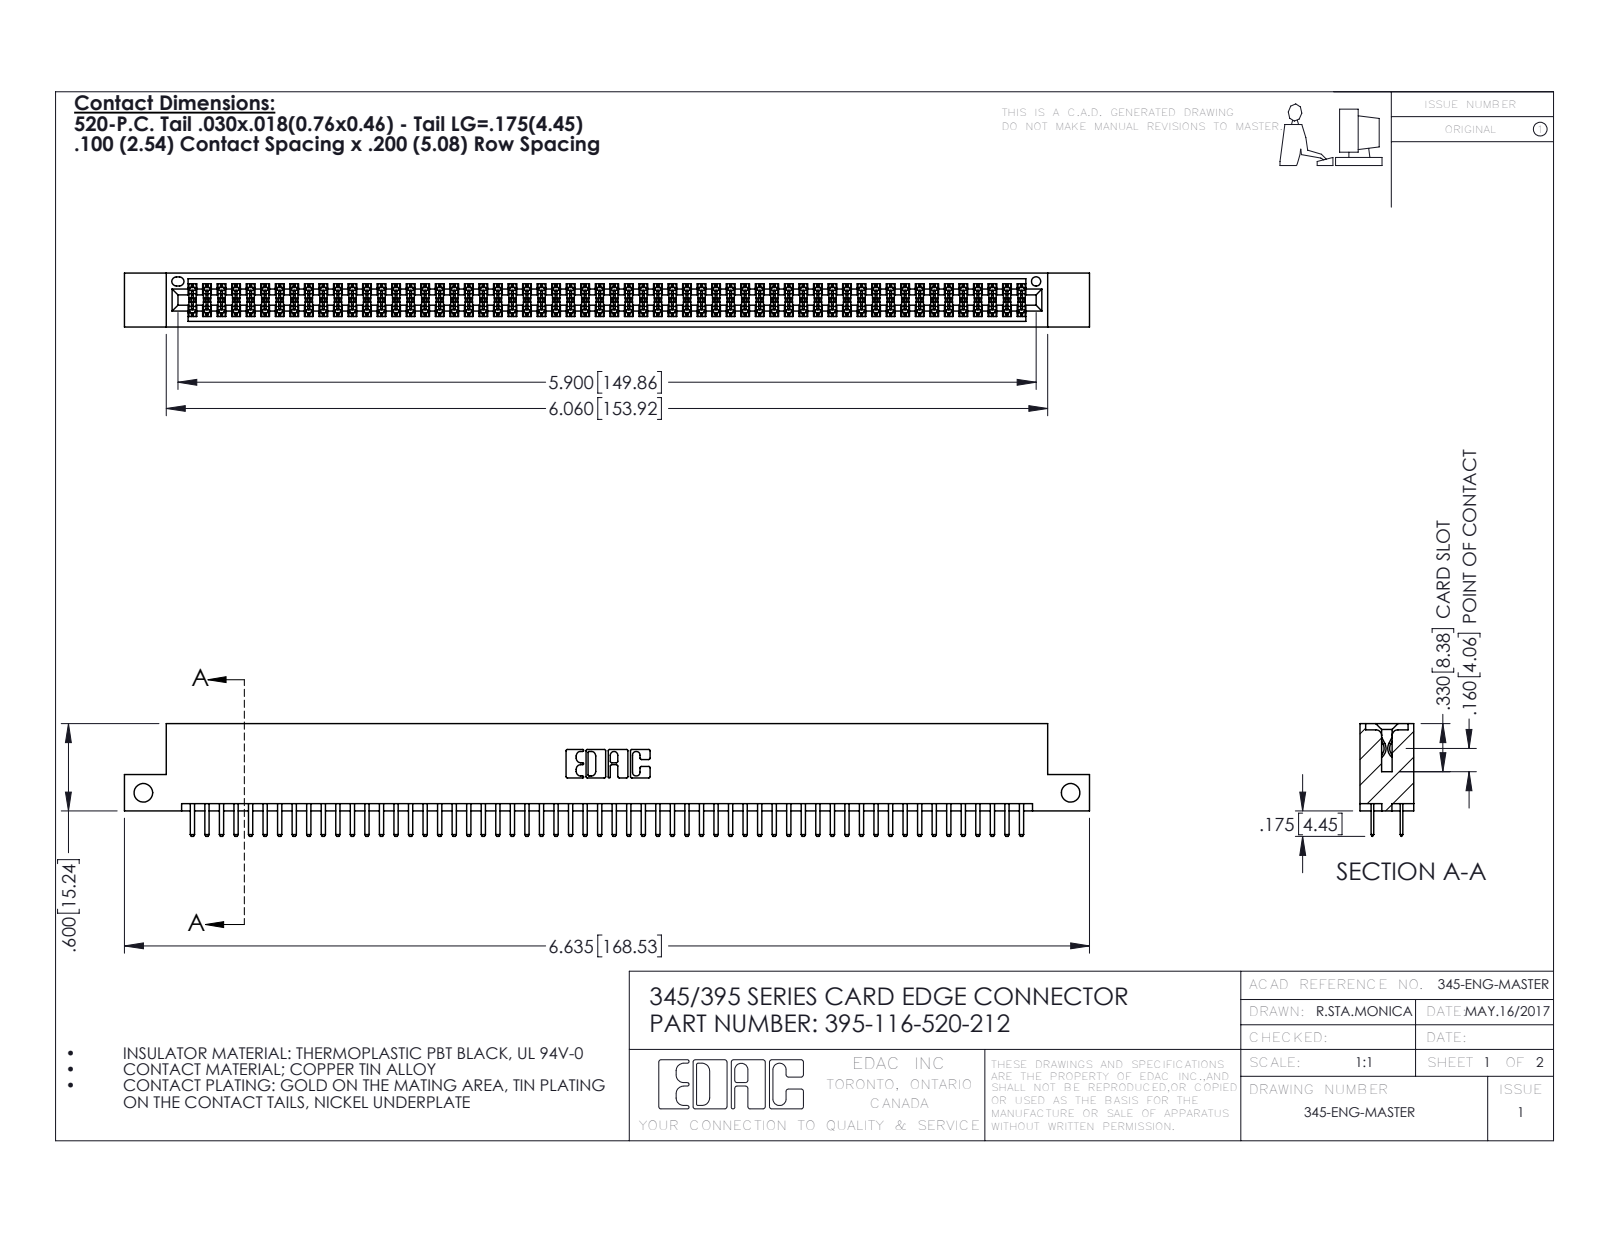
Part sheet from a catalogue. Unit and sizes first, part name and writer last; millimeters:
Units: millimetres
Overall size (bounding box): 168.5 × 19.7 × 9.4
Round holes (diameter × count): ⌀3.3 ×2, ⌀1.6 ×1
Partial cylindrical surfaces — rounded edges, fillets, slot ends (radius × count): R0.2 ×174, R0.3 ×120, R0.3 ×22, R0.2 ×6, R0.8 ×6, R0.7 ×3, R0.4 ×2, R0.5 ×2
Main face-to-face distances: 7.6, 1.8, 5.1, 9.4, 2.5, 6.9, 0.6, 5.7, 0.6, 1.8
Hole centre spacings: 161.9
Volume: 16 390 mm³ · Surface area: 24 280 mm²
Bodies: 117 solids, 6390 faces (4140 planar, 2250 cylindrical, 0 other)
Part name (STEP PRODUCT): 395-116-520-212; 345 Part_Flush Mounting Lugs - Side Mount; 345-292-001_345-293-120
STEP written by: SolidWorks 2016 (CONFIG_CONTROL_DESIGN)
